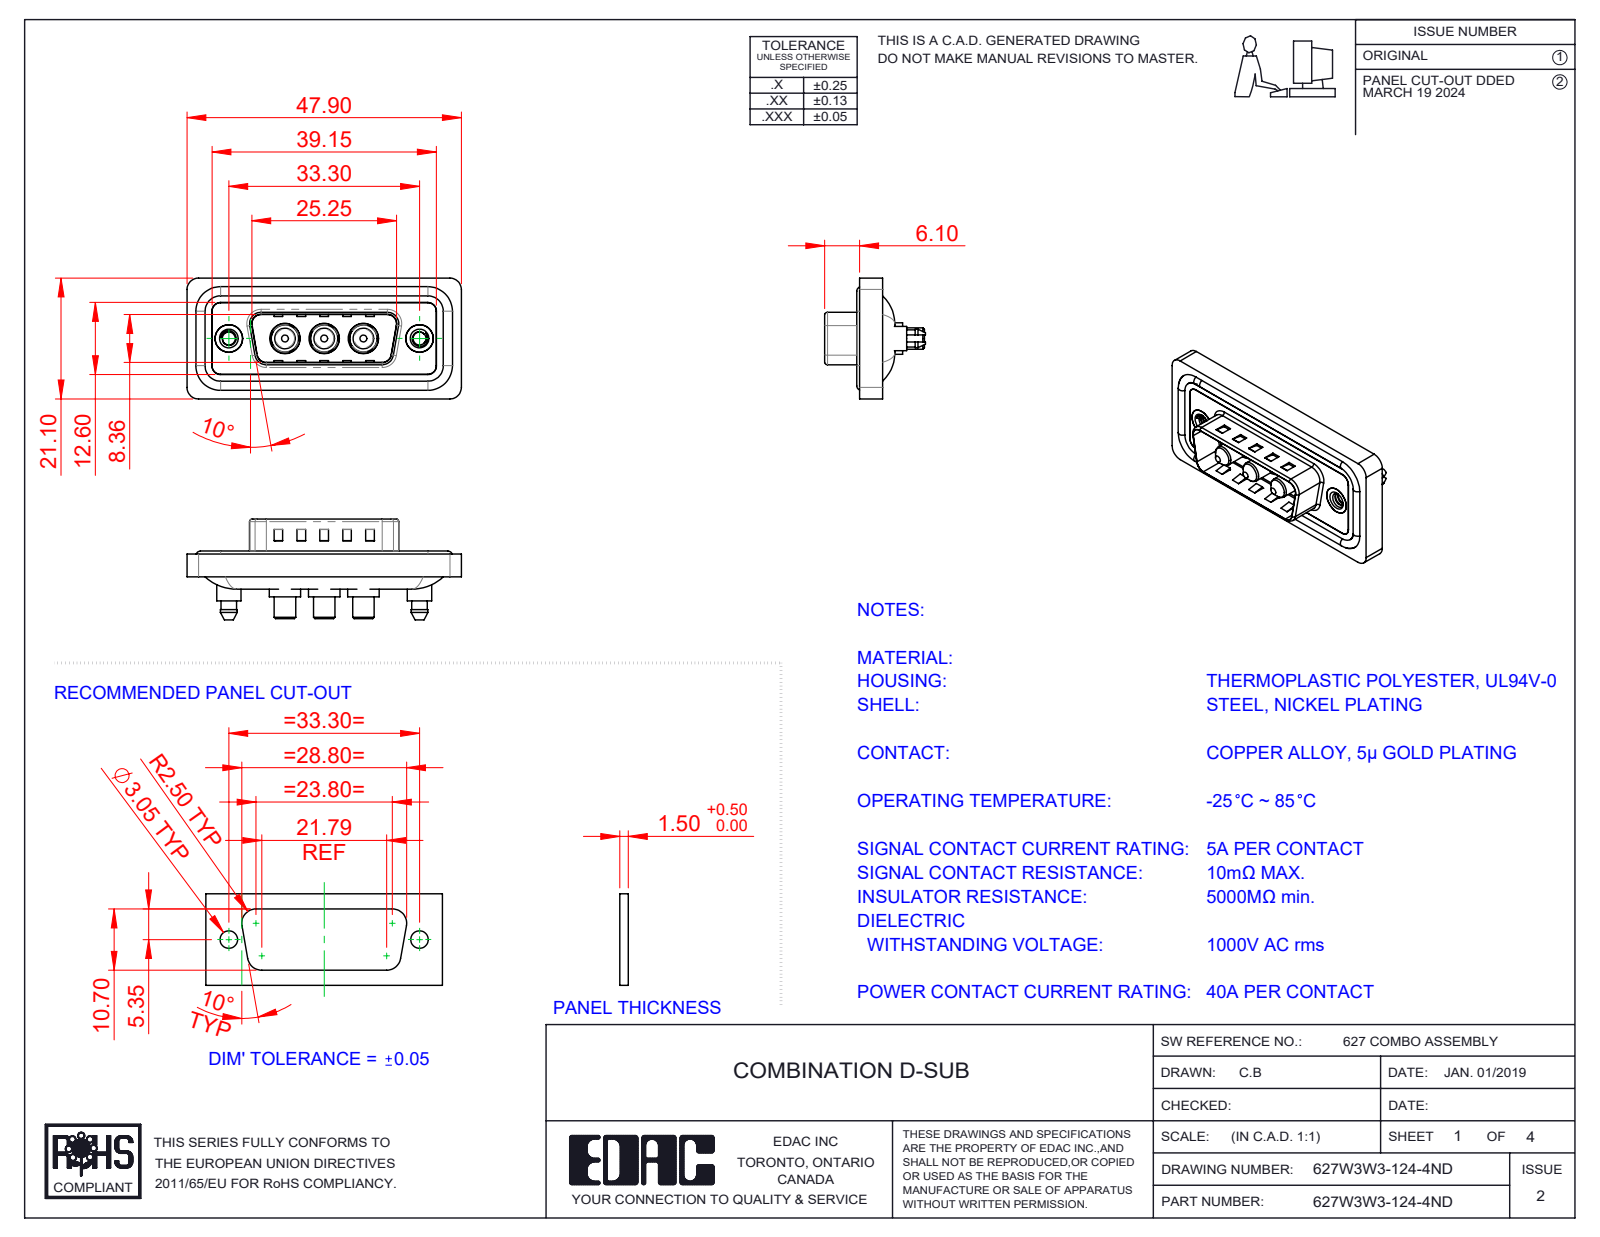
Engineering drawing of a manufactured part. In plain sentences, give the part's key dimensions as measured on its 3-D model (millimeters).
The part is named "627Combo Threaded Boardlock_5; 627W3W3-124-4ND; Power Pin_40A S; 627Combo Waterproof Housing_15 Contacts (+4 more)". Its 3-D file was written by "SolidWorks 2023 (CONFIG_CONTROL_DESIGN)". It is 13 solids with 622 faces: 223 planar, 281 cylindrical and 118 other. Overall it measures 47.9 by 21.1 by 17.6 millimeters. Its volume is 5 776 cubic millimeters and its surface area 9 122 square millimeters. Round holes: 3 of diameter 4.85, 3 of diameter 5.3, 2 of diameter 2.26, 2 of diameter 4, 2 of diameter 4.8, 2 of diameter 5. Round bosses or shafts: 4 of diameter 1.6, 3 of diameter 5.5, 3 of diameter 5.2, 3 of diameter 4.75, 3 of diameter 3.75, 3 of diameter 3.6, 2 of diameter 5.4, 2 of diameter 4.9. Partial cylindrical surfaces (rounded edges, fillets, slot ends): 28 of radius 1.5, 20 of radius 2, 10 of radius 1.6, 8 of radius 0.5, 4 of radius 0.25, 4 of radius 0.6, 4 of radius 0.65, 4 of radius 0.9. The main face-to-face distances are 0.4, 1.1, 3.1, 1.5, 1.6, 0.5, 2.9, 4, 0.7, 0.82. The hole center spacings are 6.85, 9.8, 16.65, 23.5, 13.7, 33.3.
